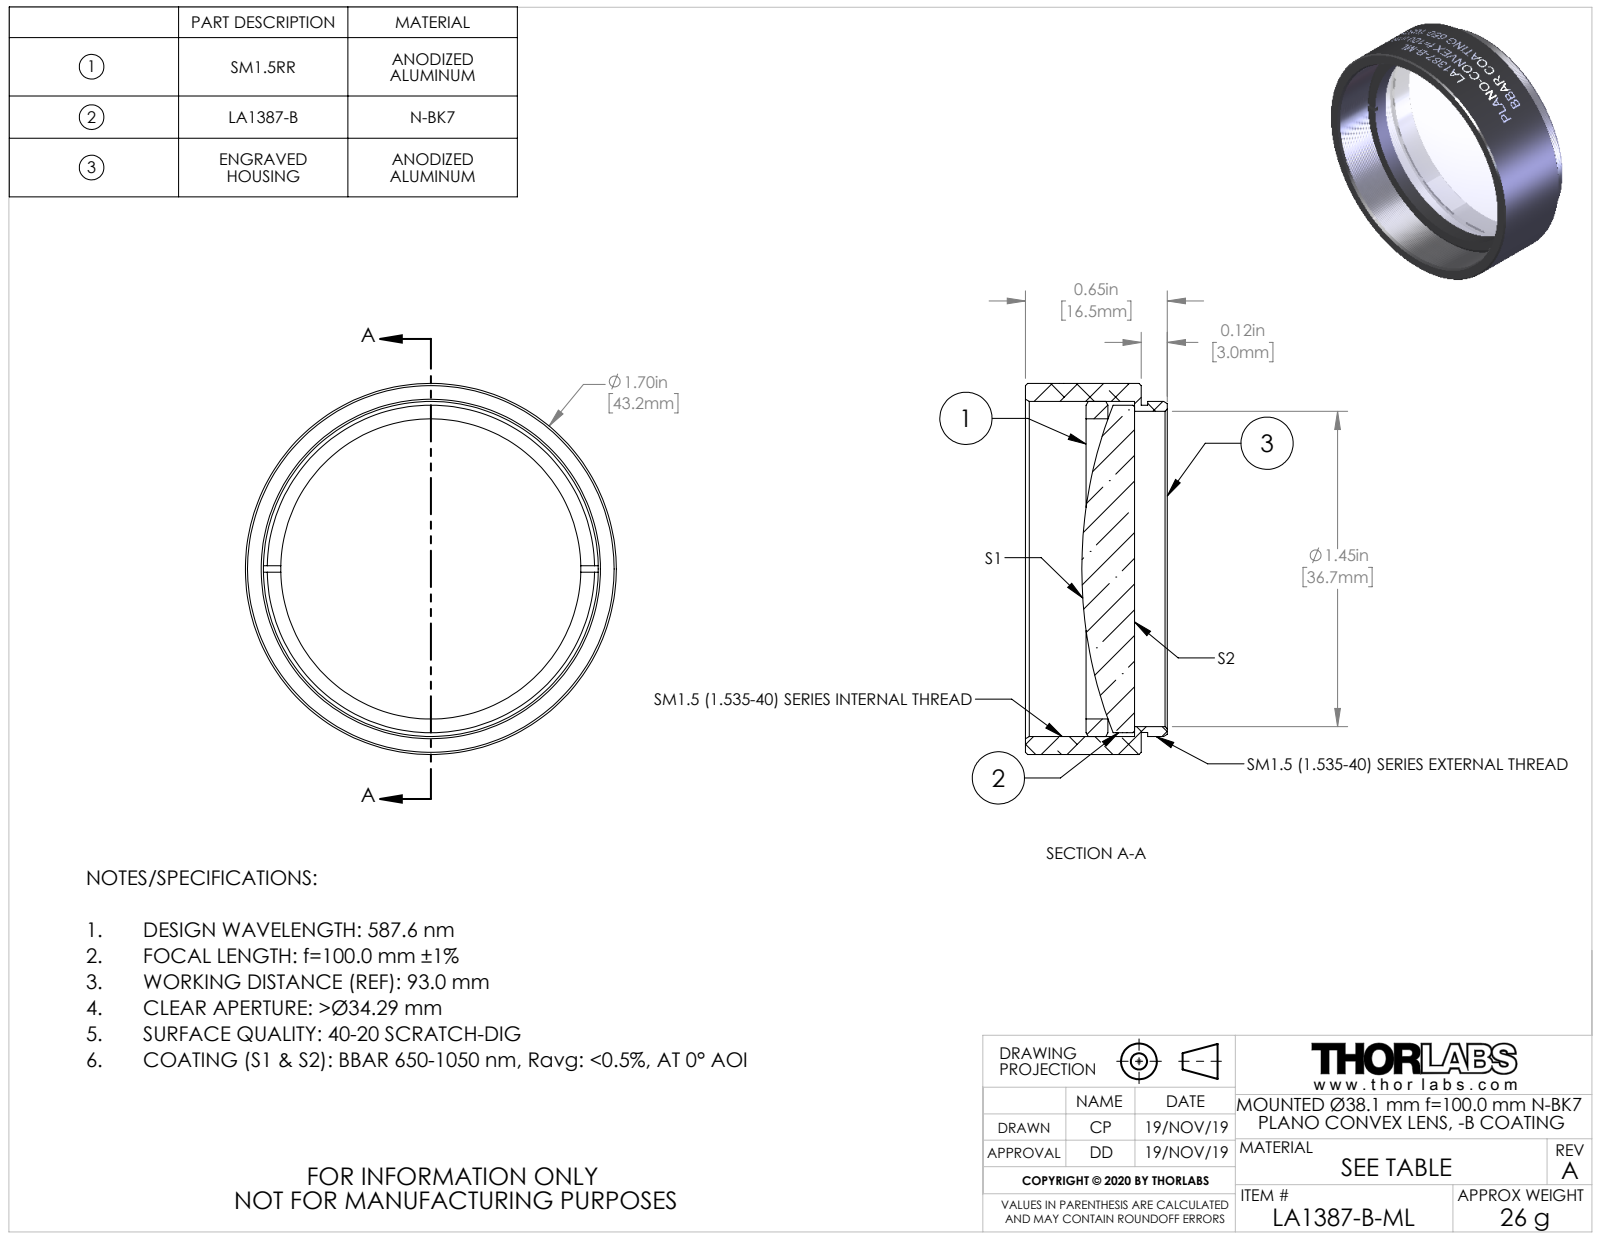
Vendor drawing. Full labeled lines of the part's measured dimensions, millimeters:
Part name (STEP PRODUCT): TTN200733-E0W
STEP written by: SolidWorks 2018 (CONFIG_CONTROL_DESIGN)
Units: millimetres
Bodies: 3 solids, 161 faces (15 planar, 127 cylindrical, 19 other)
Overall size (bounding box): 43.18 × 43.18 × 16.51
Volume: 9 623 mm³ · Surface area: 8 639 mm²
Round holes (diameter × count): ⌀34.92 ×1, ⌀36.7 ×1
Round bosses / shafts (diameter × count): ⌀43.18 ×1, ⌀38.99 ×1, ⌀38.1 ×1, ⌀38.07 ×1
Main face-to-face distances: 0.77, 13.47, 12.7, 3.87, 3.1, 9.6, 6.41, 5.64, 2.54, 7.06
